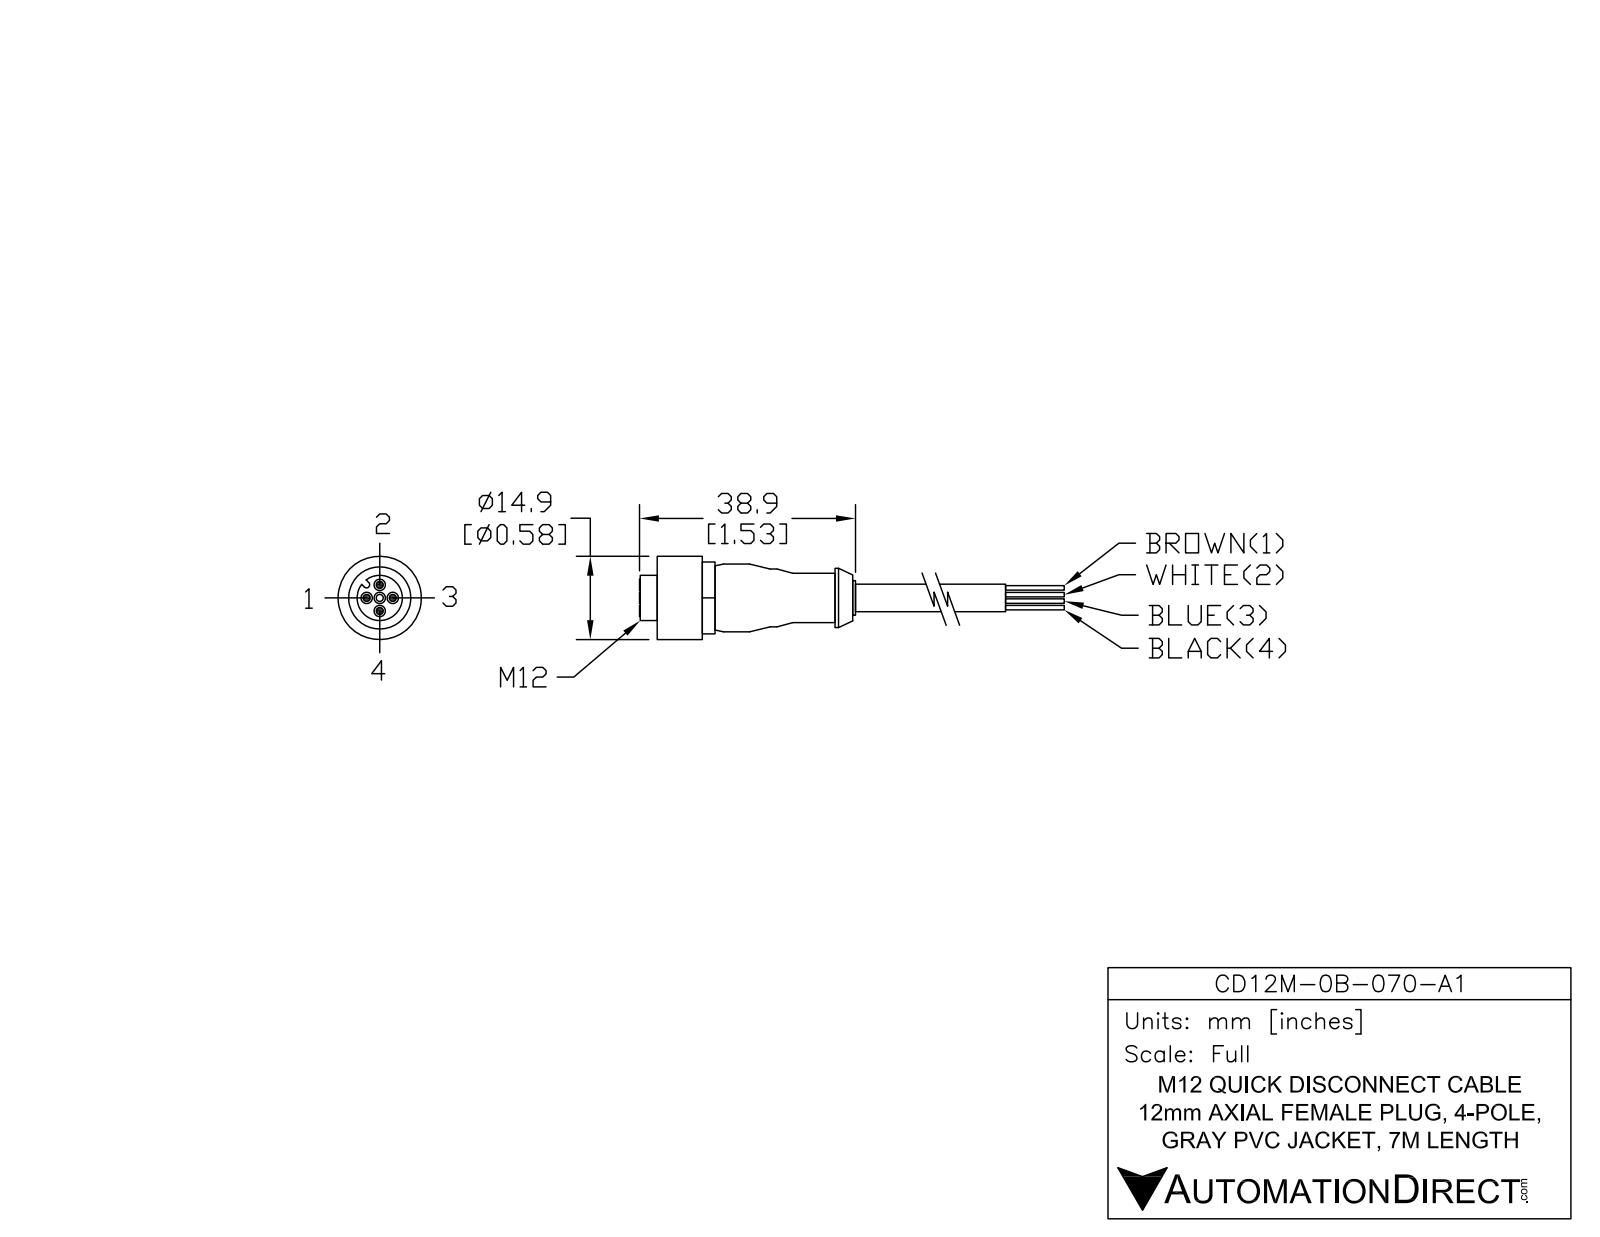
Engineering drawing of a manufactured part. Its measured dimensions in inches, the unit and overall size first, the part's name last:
Units: inches
Overall size (bounding box): 5.469 × 0.591 × 0.591
Round holes (diameter × count): ⌀0.039 ×5, ⌀0.335 ×1, ⌀0.472 ×1
Round bosses / shafts (diameter × count): ⌀0.48 ×1, ⌀0.421 ×1, ⌀0.409 ×1, ⌀0.35 ×1, ⌀0.319 ×1, ⌀0.193 ×1
Partial cylindrical surfaces — rounded edges, fillets, slot ends (radius × count): R0.022 ×1, R0.295 ×1
Main face-to-face distances: 0.996, 0.055, 0.067, 0.323, 1.051, 1.465, 0.469, 0.413, 0.256, 1.209
Hole centre spacings: 0.093, 0.131, 0.185
Volume: 0.336 in³ · Surface area: 6.947 in²
Bodies: 4 solids, 308 faces (195 planar, 107 cylindrical, 6 other)
Part name (STEP PRODUCT): CD12M-0B-070-A1
STEP written by: SolidWorks 2017 (AUTOMOTIVE_DESIGN)
